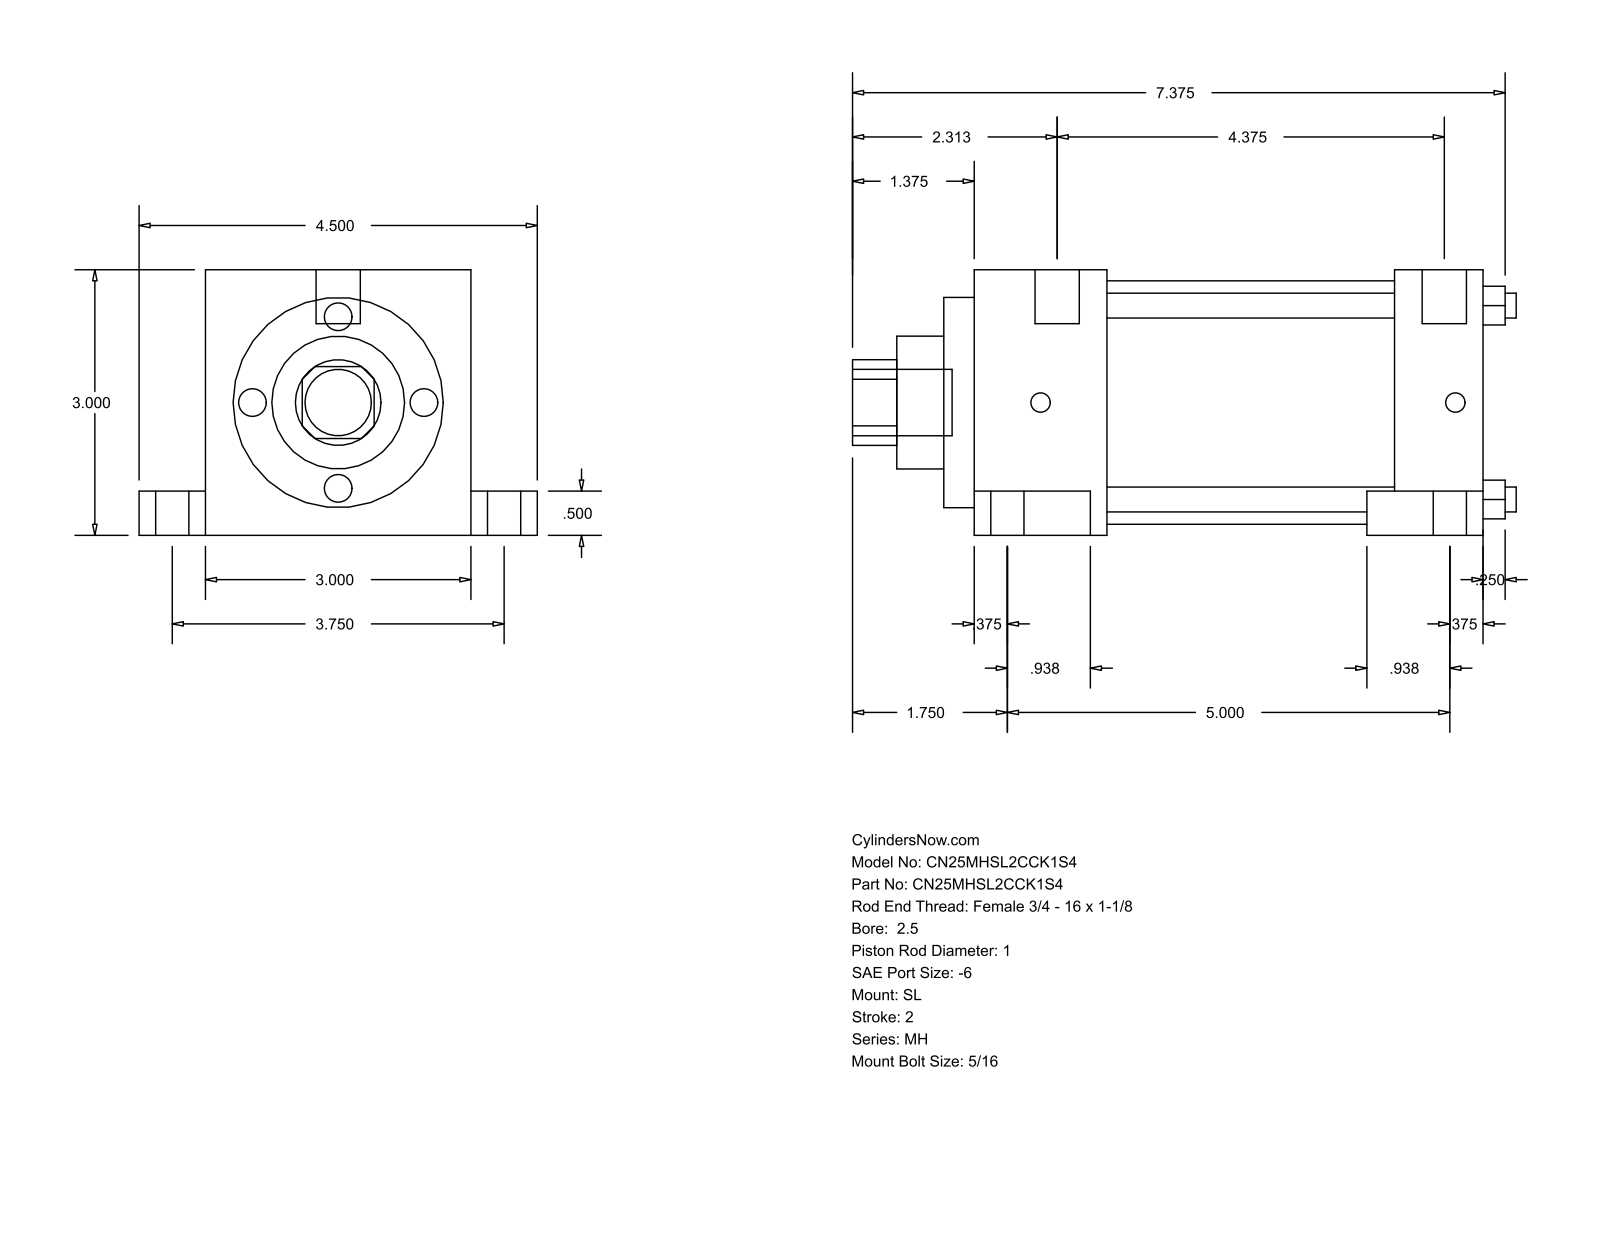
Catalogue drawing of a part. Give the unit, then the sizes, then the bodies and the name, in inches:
Units: inches
Overall size (bounding box): 7.5 × 4.5 × 3
Round holes (diameter × count): ⌀0.281 ×4, ⌀1 ×1, ⌀1.5 ×1, ⌀2.375 ×1, ⌀2.75 ×1
Round bosses / shafts (diameter × count): ⌀0.625 ×2, ⌀0.375 ×2, ⌀0.219 ×2, ⌀0.75 ×1, ⌀0.5 ×1
Partial cylindrical surfaces — rounded edges, fillets, slot ends (radius × count): R0.484 ×1
Main face-to-face distances: 3, 1, 5.094, 6.094, 0.5, 2.5, 0.75, 3.75, 0.531, 5.625
Hole centre spacings: 1.548, 2.19, 3.097
Bodies: 0 solids, 86 faces (61 planar, 25 cylindrical, 0 other)
Part name (STEP PRODUCT): MH_SL__0250_1
STEP written by: GSSL Pune (CONFIG_CONTROL_DESIGN)
